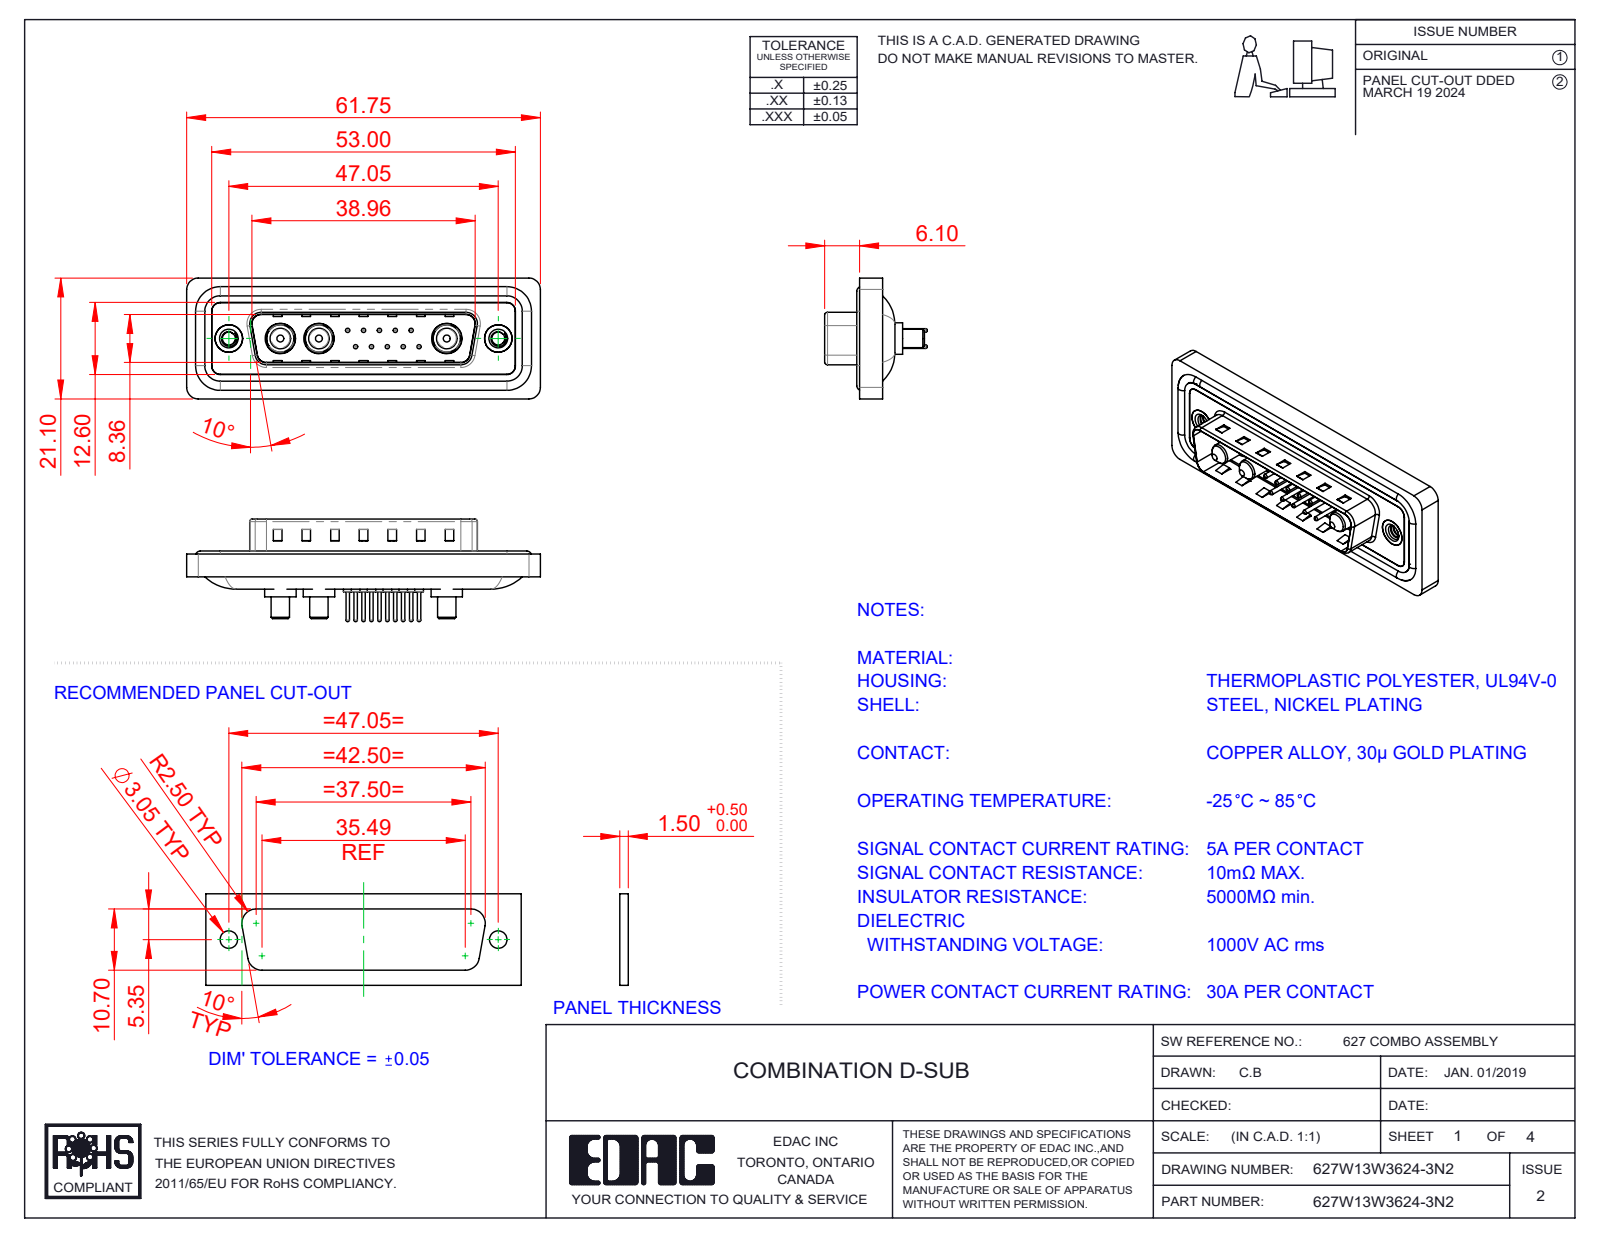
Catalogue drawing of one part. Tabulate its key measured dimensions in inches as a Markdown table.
| quantity | value |
| --- | --- |
| part name | 627Combo Housing_13W3; 627Combo Shell Rear_25 Contacts; 627W13W3624-3N2; 627Combo Contact Row 1_24 (+5 more) |
| STEP written by | SolidWorks 2023 (CONFIG_CONTROL_DESIGN) |
| units | inches |
| bodies | 23 solids, 970 faces (309 planar, 385 cylindrical, 276 other) |
| overall size | 2.431 × 0.831 × 0.705 |
| volume | 0.449 in³ |
| surface area | 18.43 in² |
| round holes (diameter × count) | 0.03 × 10, 0.063 × 10, 0.079 × 10, 0.191 × 3, 0.209 × 3, 0.089 × 2, 0.157 × 2, 0.189 × 2, 0.197 × 2 |
| round bosses / shafts (diameter × count) | 0.059 × 10, 0.024 × 10, 0.063 × 4, 0.217 × 3, 0.205 × 3, 0.187 × 3, 0.148 × 3, 0.142 × 3 |
| partial cylindrical surfaces (radius × count) | 0.059 × 22, 0.079 × 18, 0.02 × 8, 0.063 × 8, 0.01 × 4, 0.024 × 4, 0.026 × 4, 0.035 × 4 |
| main face-to-face distances | 0.016, 0.059, 0.043, 0.063, 0.02, 0.122, 0.114, 0.032, 0.377, 0.161 |
| hole center spacings | 0.124, 0.109, 0.198, 0.218, 0.295, 0.198, 0.327, 0.398 |
